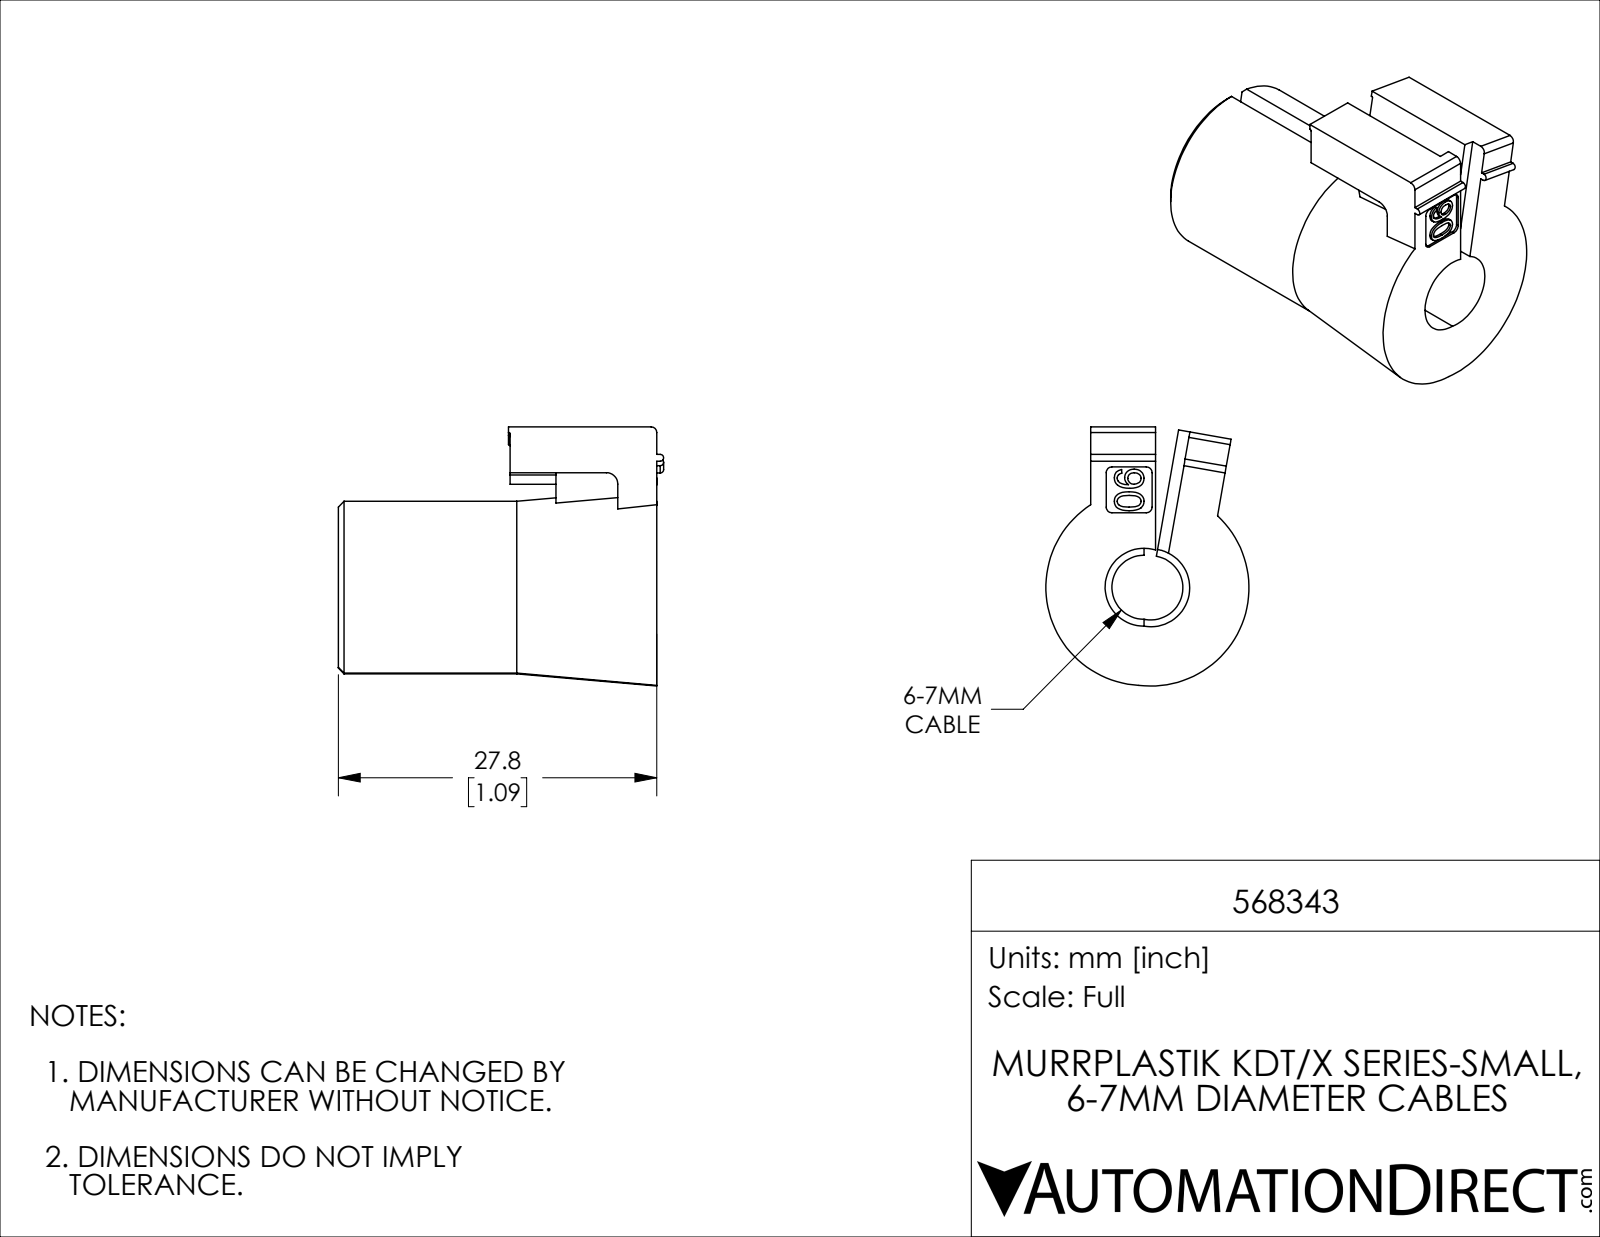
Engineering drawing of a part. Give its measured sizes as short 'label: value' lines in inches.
name: 568343
written by: SolidWorks 2019 (CONFIG_CONTROL_DESIGN)
unit: in
bodies: 1 solid, 112 faces (49 planar, 24 cylindrical, 39 other)
size: 1.118 × 0.891 × 0.698
volume: 0.292 in³; area: 4.72 in²
rounds: 6× R0.02, 2× R0.004, 2× R0.012, 2× R0.039, 2× R0.11, 2× R0.134, 2× R0.295
face distances: 0.183, 1.094, 0.157, 0.039, 0.504, 0.591, 0.059, 0.445, 1.035, 0.144
